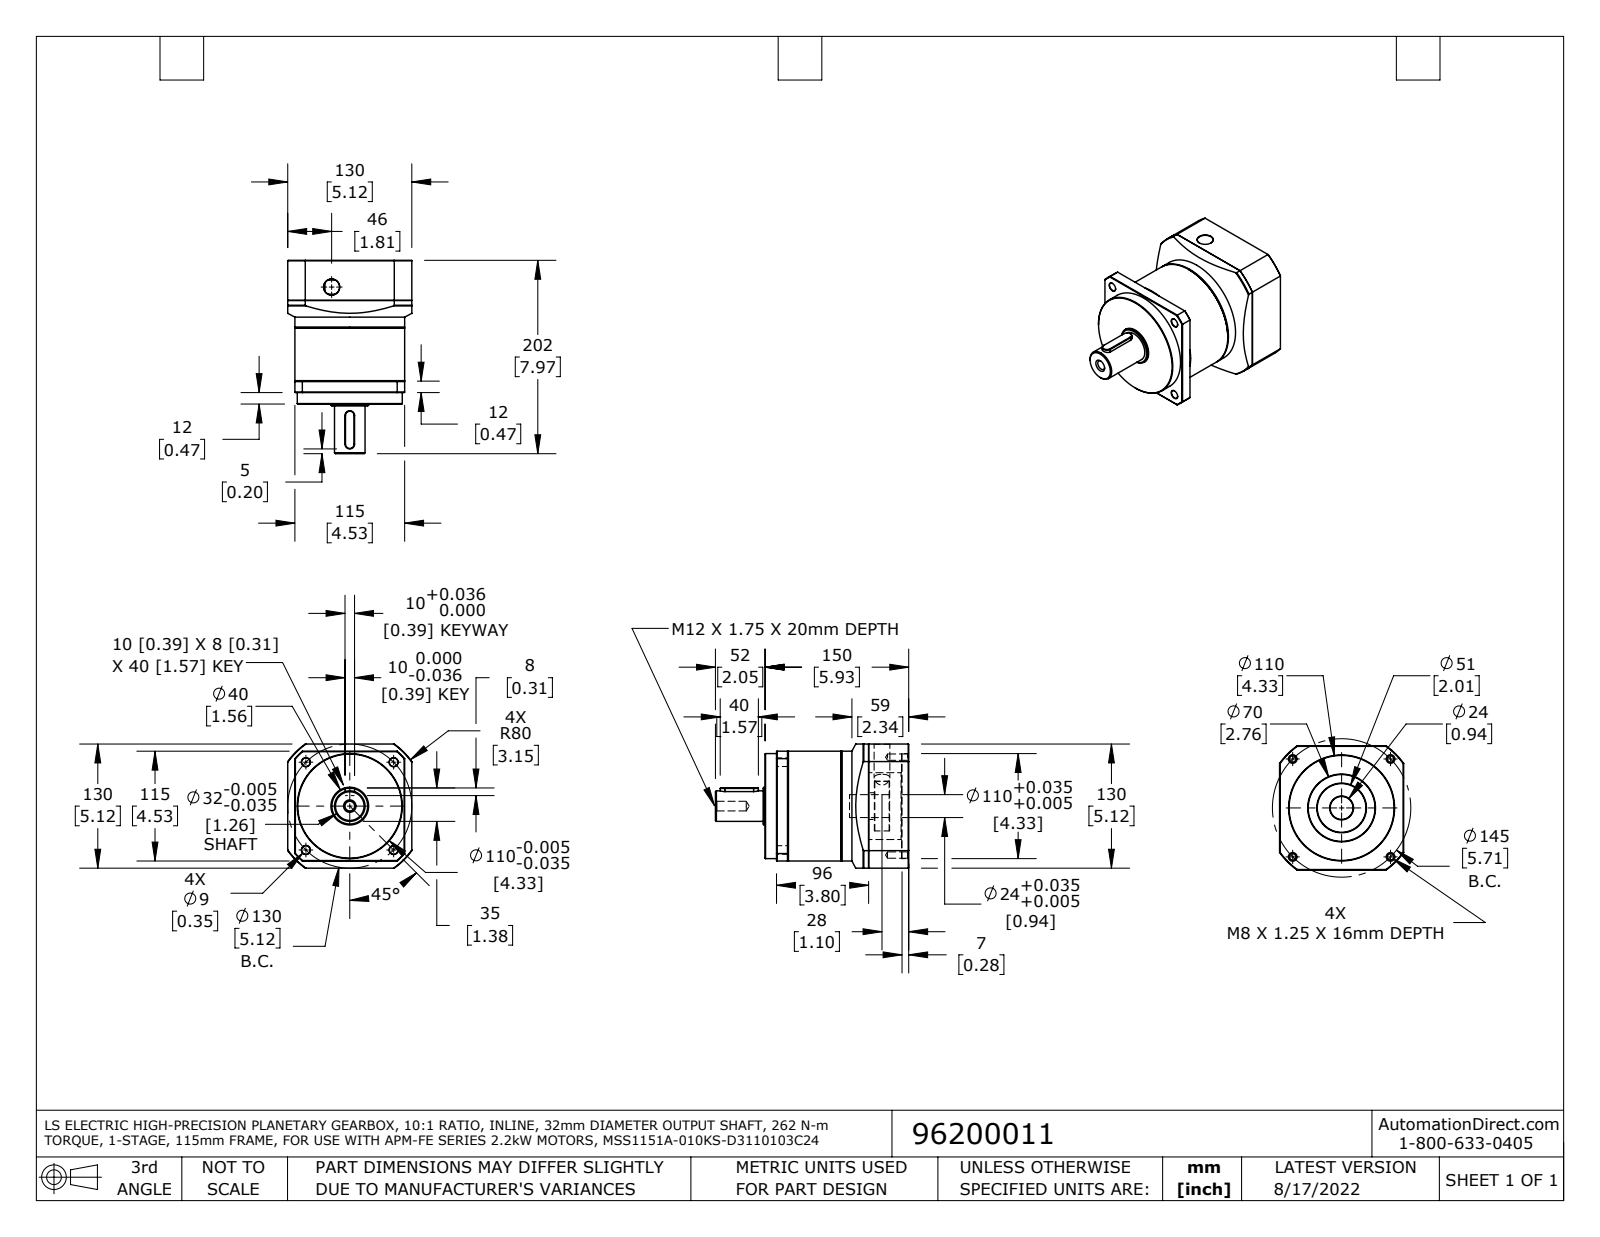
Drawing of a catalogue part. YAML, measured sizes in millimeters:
part_name: "MSS1151A-D3110103 nc fxt"
step_written_by: "SolidWorks 2021 (AUTOMOTIVE_DESIGN)"
units: millimeters
bodies: {solids: 3, faces: 181, planar: 46, cylindrical: 54, other: 81}
overall_size: [202.5, 130, 130]
volume: 1750000
surface_area: 172000
round_holes:
  - {diameter: 6.7, count: 4}
  - {diameter: 9, count: 4}
  - {diameter: 10.1, count: 1}
  - {diameter: 16.5, count: 1}
  - {diameter: 24, count: 1}
  - {diameter: 70, count: 1}
  - {diameter: 110, count: 1}
round_bosses_or_shafts:
  - {diameter: 115, count: 1}
  - {diameter: 52, count: 1}
  - {diameter: 39.5, count: 1}
  - {diameter: 32, count: 1}
  - {diameter: 28, count: 1}
partial_cylinders:
  - {radius: 5, count: 2}
  - {radius: 76, count: 1}
  - {radius: 80, count: 1}
face_to_face_distances: [28.5, 7.5, 130, 108.5, 80, 34.5, 42, 70.5, 150.5, 63]
hole_center_spacings: [97.4, 65, 91.9, 137.5, 7.5, 7.5, 72.5, 72.5]
